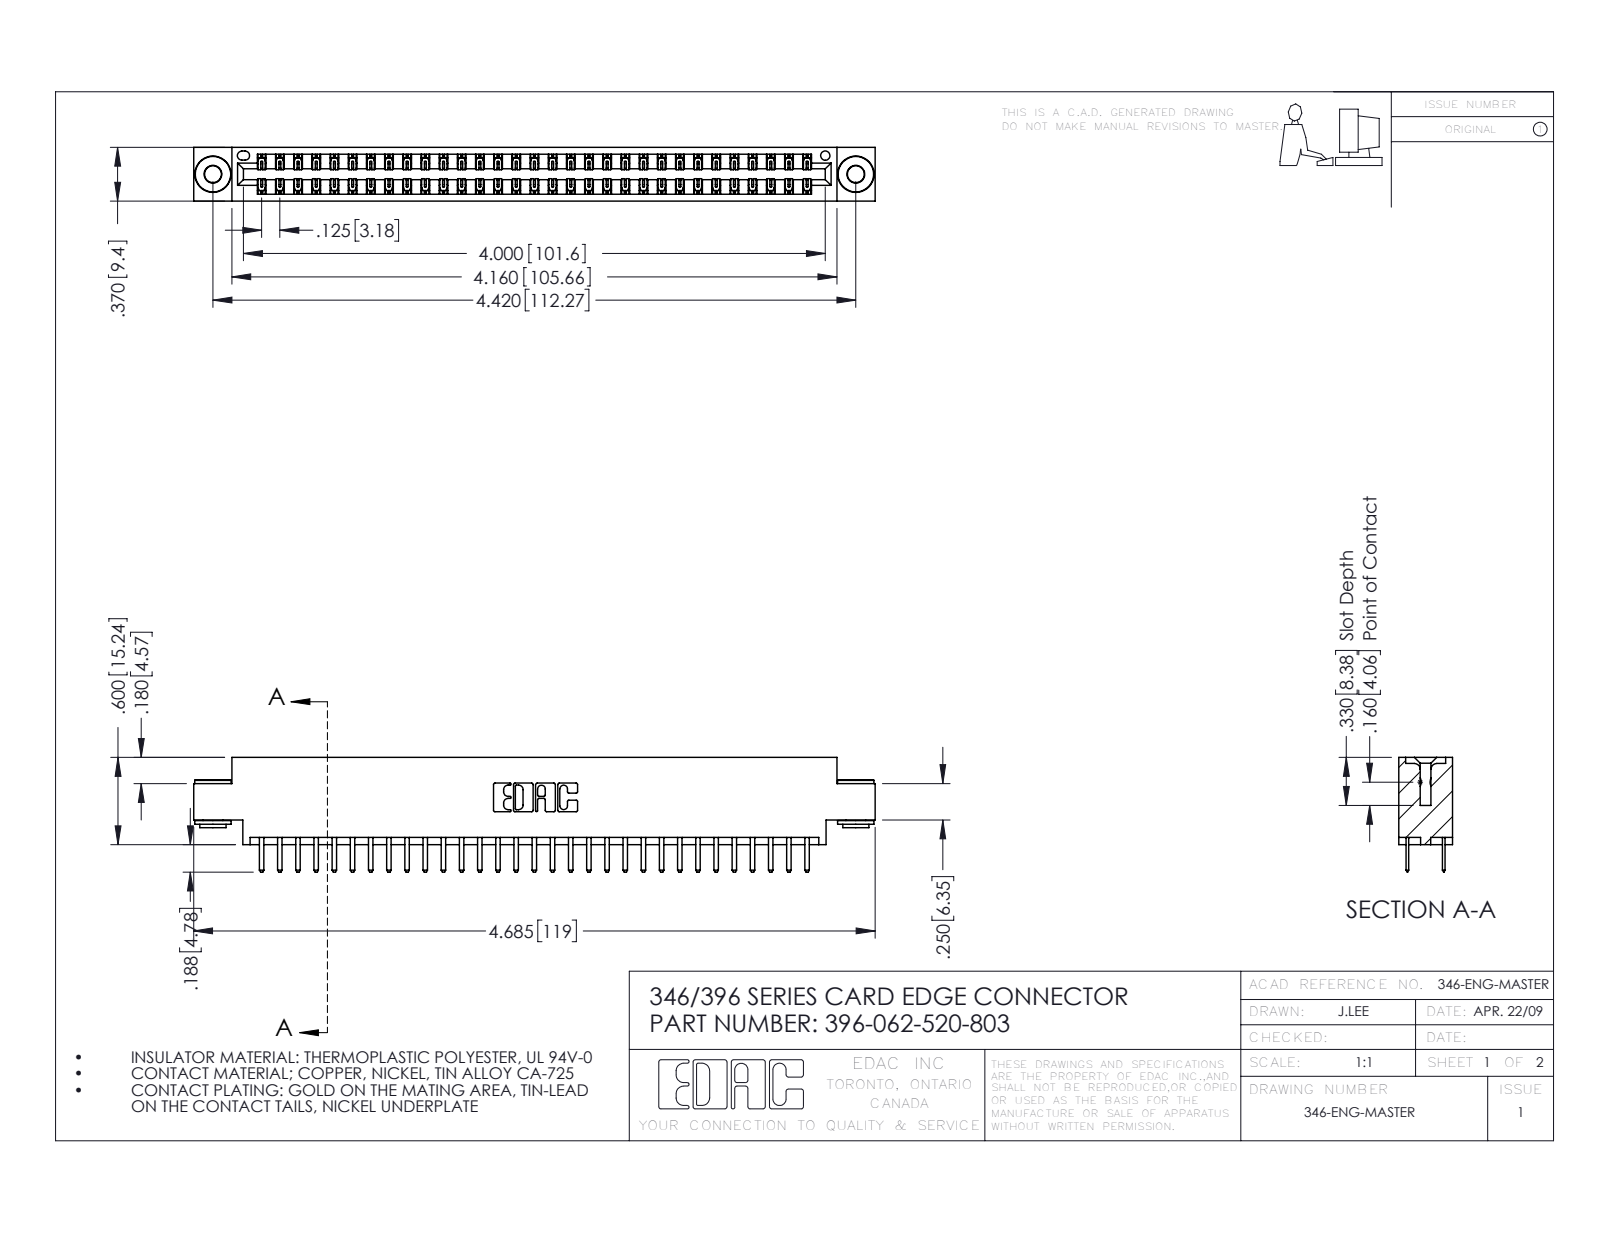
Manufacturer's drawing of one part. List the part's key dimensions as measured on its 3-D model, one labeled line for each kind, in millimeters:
Part name (STEP PRODUCT): 396-062-520-803; 346 Part_0.170 Offset - 0.156 Dia-TH; 345-250-002_345-250-002-102; 345-292-001_345-293-120
STEP written by: SolidWorks 2016 (CONFIG_CONTROL_DESIGN)
Units: millimetres
Bodies: 65 solids, 3636 faces (2384 planar, 1244 cylindrical, 8 other)
Overall size (bounding box): 119 × 20 × 9.4
Volume: 11 400 mm³ · Surface area: 15 770 mm²
Round holes (diameter × count): ⌀2.9 ×2, ⌀4 ×2, ⌀1.6 ×1
Round bosses / shafts (diameter × count): ⌀6.4 ×2, ⌀4.6 ×2, ⌀3.5 ×2
Partial cylindrical surfaces — rounded edges, fillets, slot ends (radius × count): R0.2 ×93, R0.3 ×66, R0.3 ×22, R0.2 ×6, R0.8 ×6, R0.7 ×3, R0.4 ×2, R0.6 ×2
Main face-to-face distances: 1.2, 8.2, 9.4, 6.4, 0.6, 7, 1.8, 7.6, 3.8, 5.6
Hole centre spacings: 6.2, 107, 112.3
